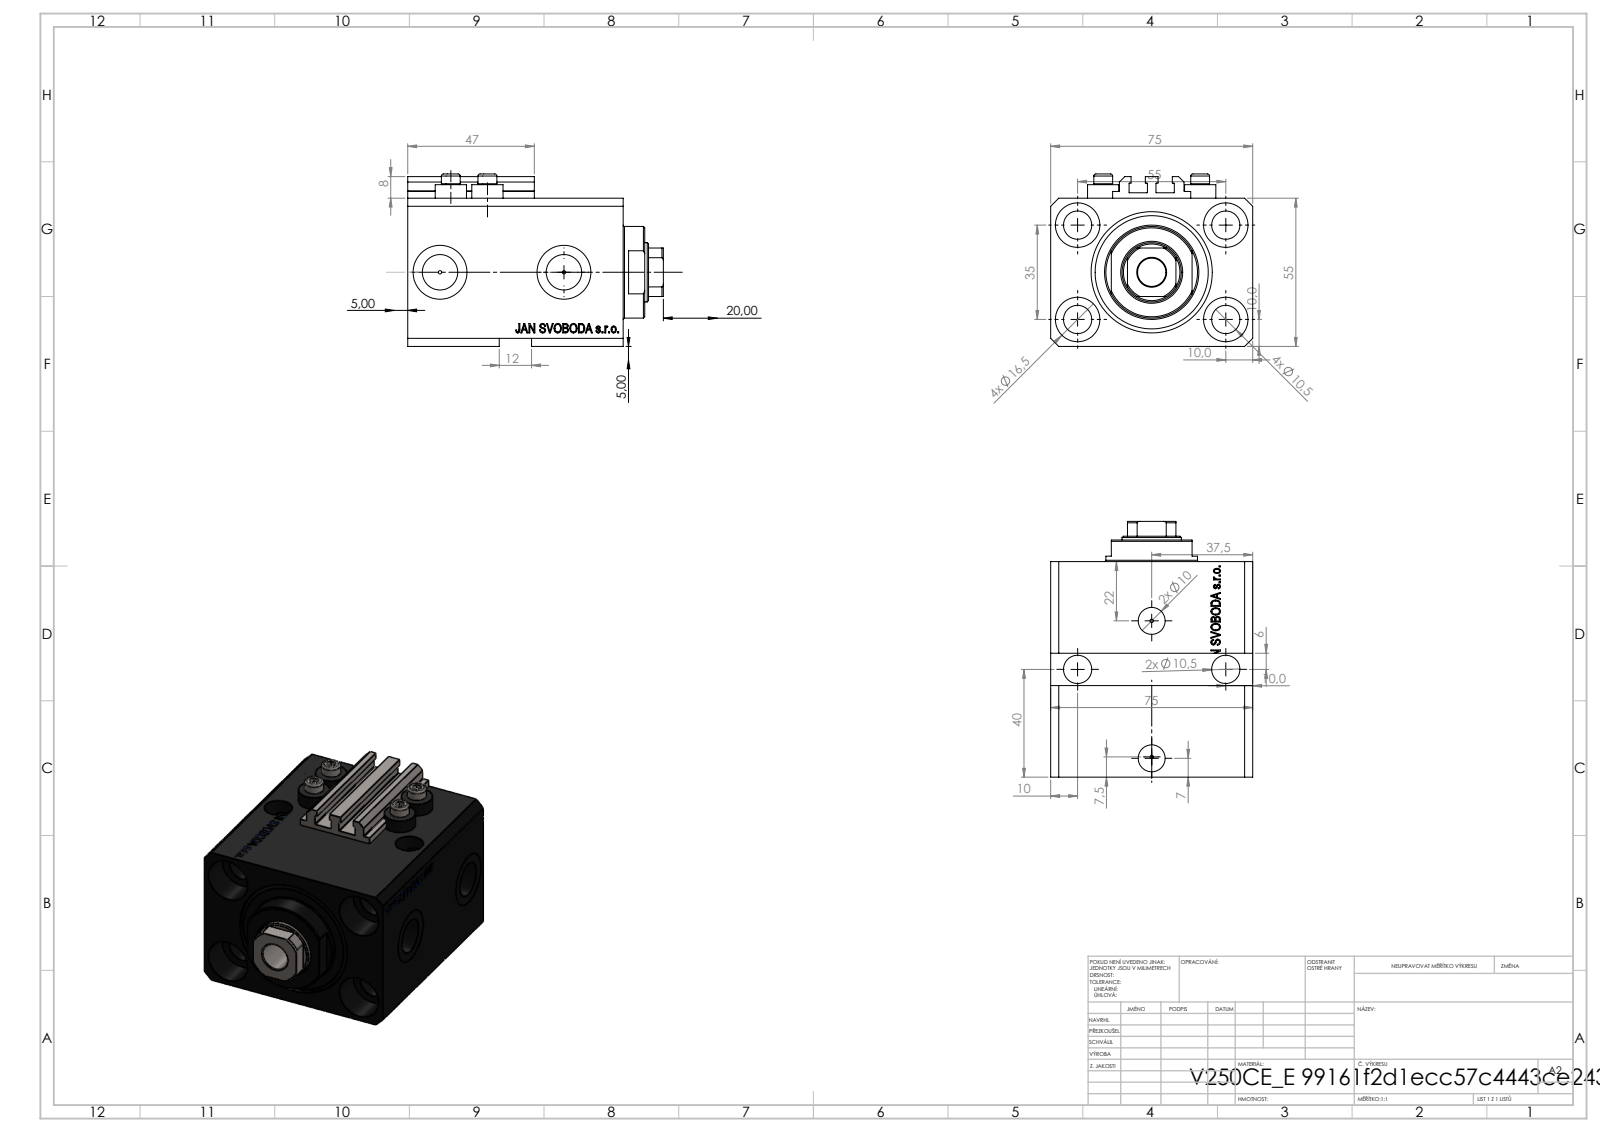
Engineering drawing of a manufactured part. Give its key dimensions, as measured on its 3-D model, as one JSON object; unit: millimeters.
{"part_name": "ALLEN BOLT V250CE; V250CE_E_Body; V250CE_C_VCP; V250CE_VC_E", "step_written_by": "SolidWorks 2019 (CONFIG_CONTROL_DESIGN)", "units": "millimeters", "bodies": {"solids": 8, "faces": 1080, "planar": 518, "cylindrical": 138, "other": 424}, "overall_size": [95, 75, 64], "volume_mm3": 280274, "surface_area_mm2": 75612, "round_holes": [[10.5, 7], [1.25, 4], [4, 4], [16.5, 4], [10, 2], [13.16, 2], [20, 2], [22, 1], [32, 1], [45, 1]], "round_bosses_or_shafts": [[11.6, 4], [7, 4], [34, 1]], "partial_cylinders_radius": [[0.2, 10], [10.5, 1]], "face_to_face_distances": [55, 75, 15, 80, 65, 3, 9.9, 55.1, 70.1, 54], "hole_center_spacings": [32.6, 55, 13.6, 14.09, 19.89, 20.12, 25.81, 28.48]}
